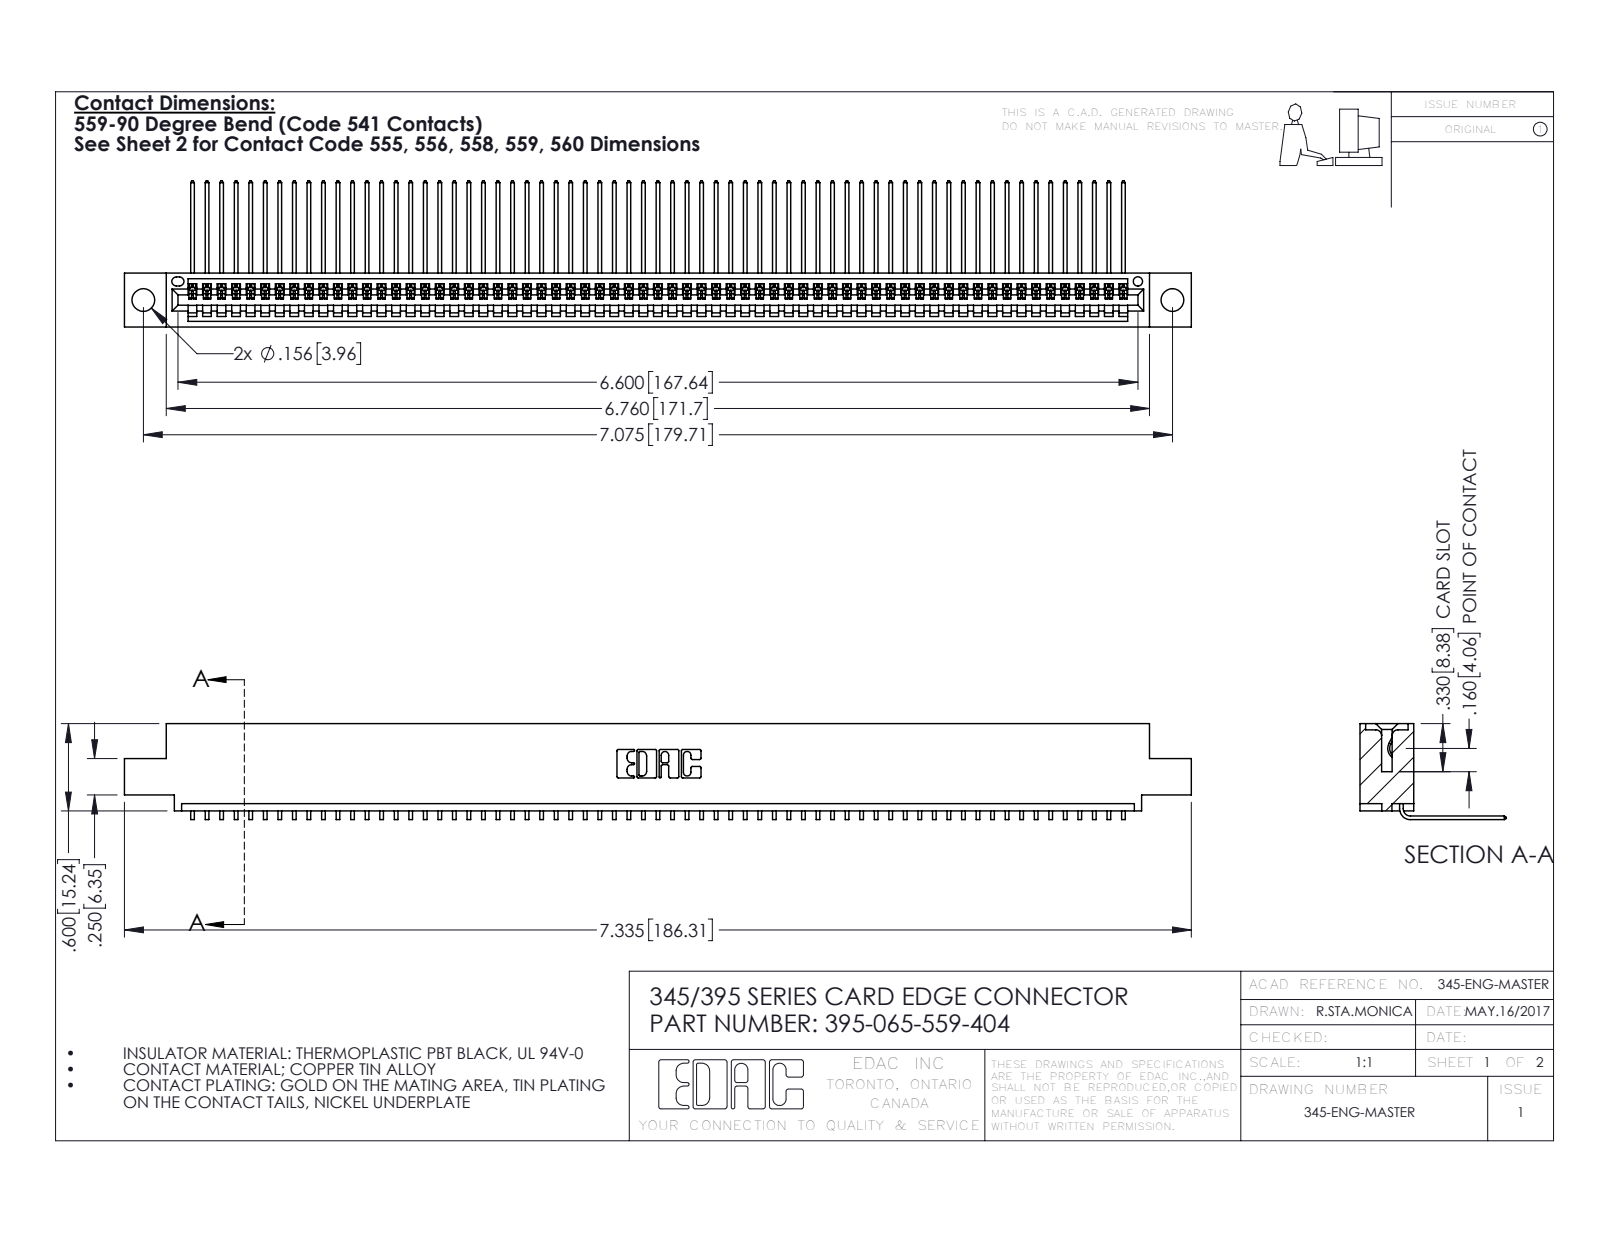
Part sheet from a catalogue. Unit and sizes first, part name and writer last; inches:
Units: inches
Overall size (bounding box): 7.335 × 1.005 × 0.659
Round holes (diameter × count): ⌀0.156 ×2, ⌀0.064 ×1
Partial cylindrical surfaces — rounded edges, fillets, slot ends (radius × count): R0.006 ×130, R0.01 ×22, R0.007 ×6, R0.031 ×6, R0.026 ×3, R0.031 ×2, R0.04 ×2, R0.014 ×1
Main face-to-face distances: 0.072, 0.298, 0.37, 0.2, 0.098, 0.272, 0.025, 0.225, 0.149, 0.072
Hole centre spacings: 0.27, 6.839, 7.075
Volume: 1.095 in³ · Surface area: 39.24 in²
Bodies: 66 solids, 4030 faces (2814 planar, 1216 cylindrical, 0 other)
Part name (STEP PRODUCT): 345-292-001_558 559 Tail - 1; 395-065-559-404; 345 Part_0.110 Offset - 0.156 Dia-TH
STEP written by: SolidWorks 2016 (CONFIG_CONTROL_DESIGN)
